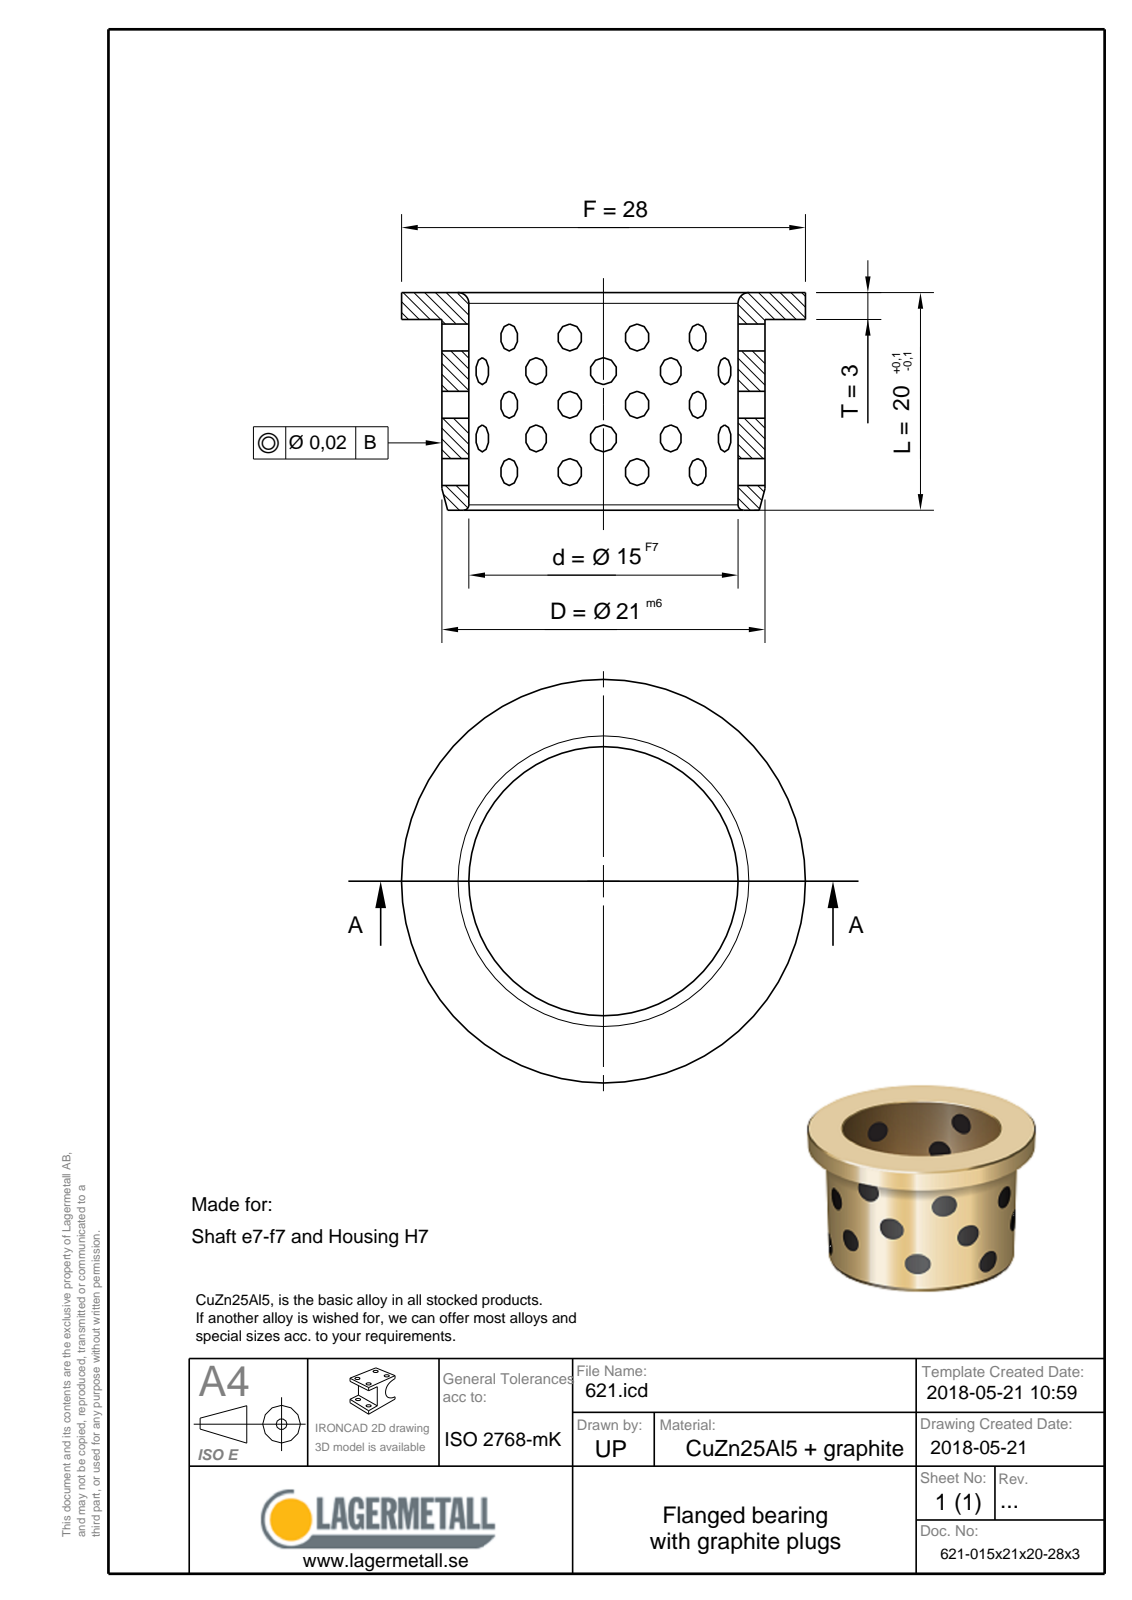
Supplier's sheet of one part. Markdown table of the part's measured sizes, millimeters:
| quantity | value |
| --- | --- |
| part name | 621-015x21x20-28x3 |
| STEP written by | Spatial InterOp 3D (CONFIG_CONTROL_DESIGN) |
| units | millimeters |
| bodies | 1 solid, 9 faces (3 planar, 3 cylindrical, 3 other) |
| overall size | 28 × 28 × 20 |
| volume | 4 108 mm³ |
| surface area | 3 104 mm² |
| round holes (diameter × count) | 15 × 1 |
| round bosses / shafts (diameter × count) | 28 × 1, 21 × 1 |
| main face-to-face distances | 3, 17, 20 |
